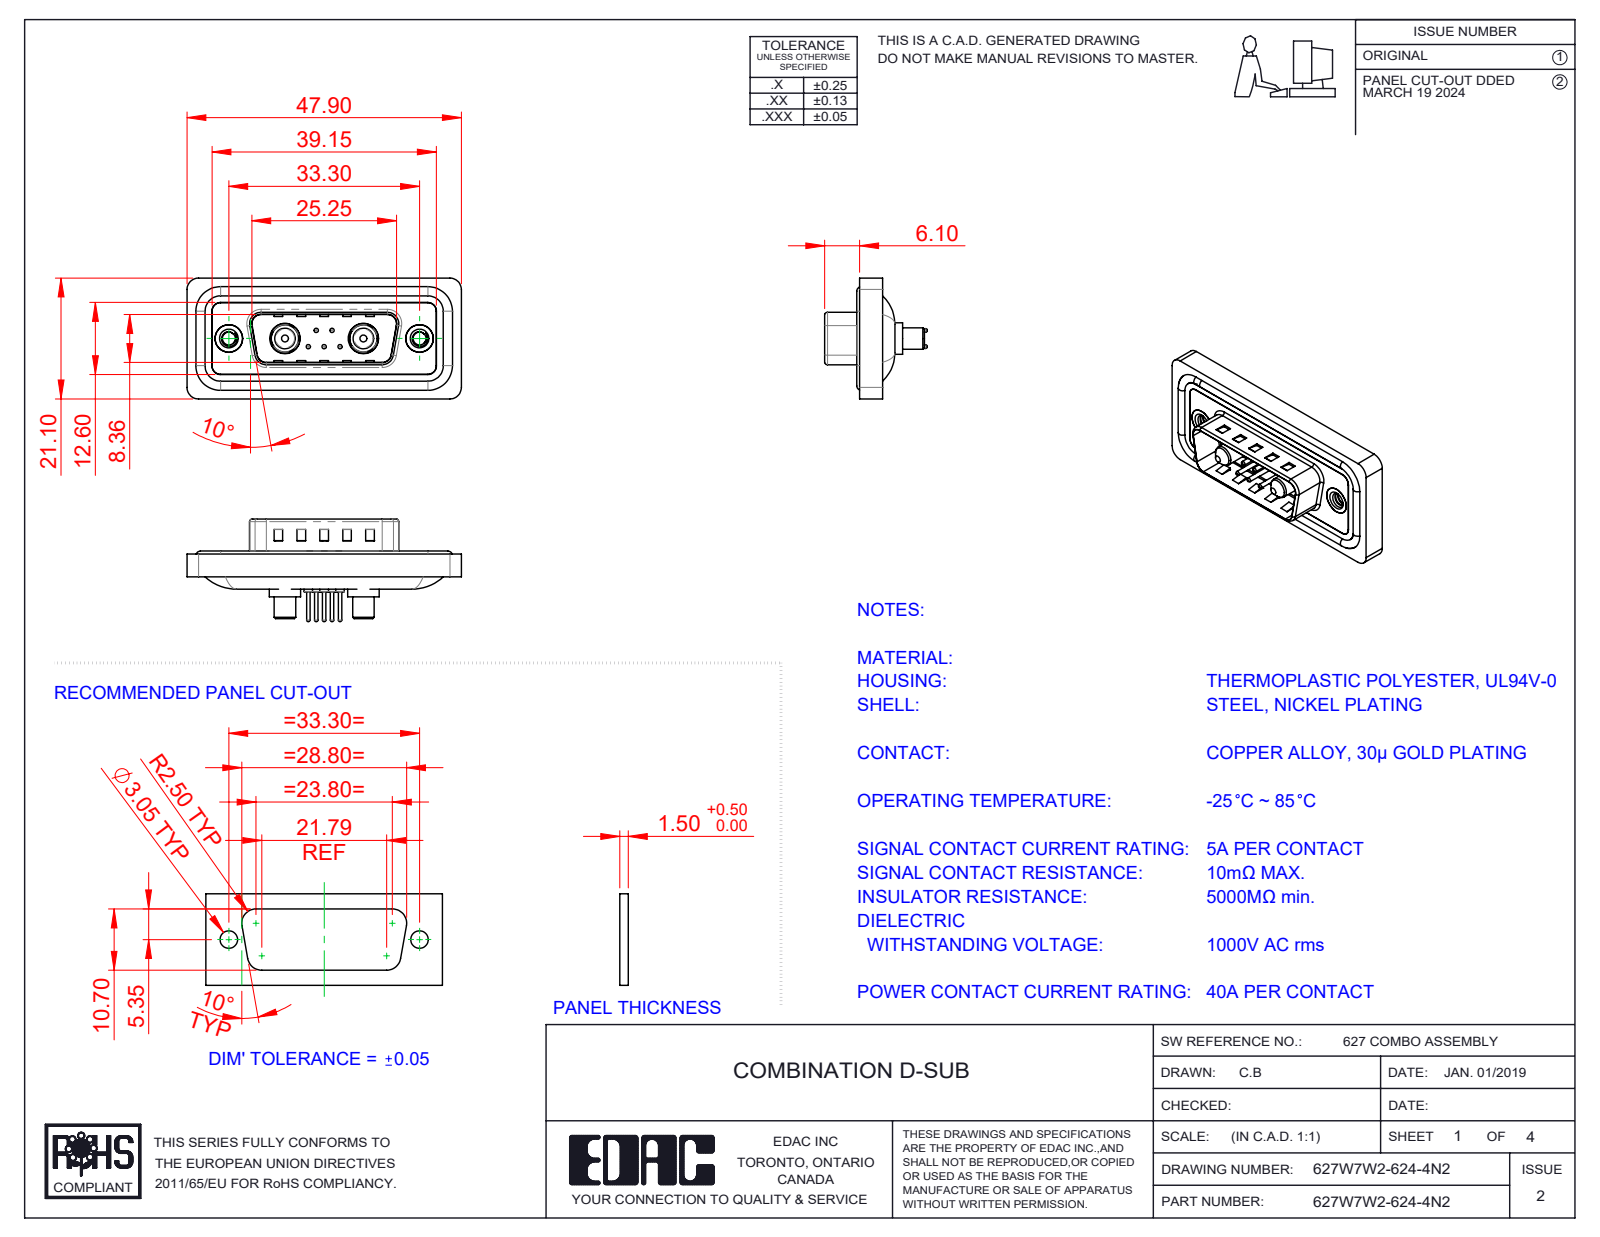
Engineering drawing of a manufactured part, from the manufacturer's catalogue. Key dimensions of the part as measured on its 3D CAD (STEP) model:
Part name (STEP PRODUCT): 627Combo Waterproof Housing_15 Contacts; 627W7W2-624-4N2; 627Combo Contact Row 1_24; 627Combo Shell Front_15 Contacts (+5 more)
STEP written by: SolidWorks 2023 (CONFIG_CONTROL_DESIGN)
Units: millimetres
Bodies: 16 solids, 710 faces (232 planar, 292 cylindrical, 186 other)
Overall size (bounding box): 47.9 × 21.1 × 17.9
Volume: 5 554 mm³ · Surface area: 8 815 mm²
Round holes (diameter × count): ⌀0.75 ×5, ⌀1.6 ×5, ⌀2 ×5, ⌀2.26 ×2, ⌀4 ×2, ⌀4.8 ×2, ⌀4.85 ×2, ⌀5 ×2, ⌀5.3 ×2
Round bosses / shafts (diameter × count): ⌀1.5 ×5, ⌀0.6 ×5, ⌀1.6 ×4, ⌀5.5 ×2, ⌀5.2 ×2, ⌀4.9 ×2, ⌀4.75 ×2, ⌀3.75 ×2
Partial cylindrical surfaces — rounded edges, fillets, slot ends (radius × count): R1.5 ×26, R2 ×20, R0.5 ×8, R1.6 ×8, R0.25 ×4, R0.6 ×4, R0.65 ×4, R0.9 ×4
Main face-to-face distances: 0.4, 1.1, 1.6, 1.5, 0.5, 3.1, 2.9, 0.82, 9.58, 2.5
Hole centre spacings: 3.16, 2.77, 9.8, 23.5, 4.31, 4.33, 5.03, 5.04
